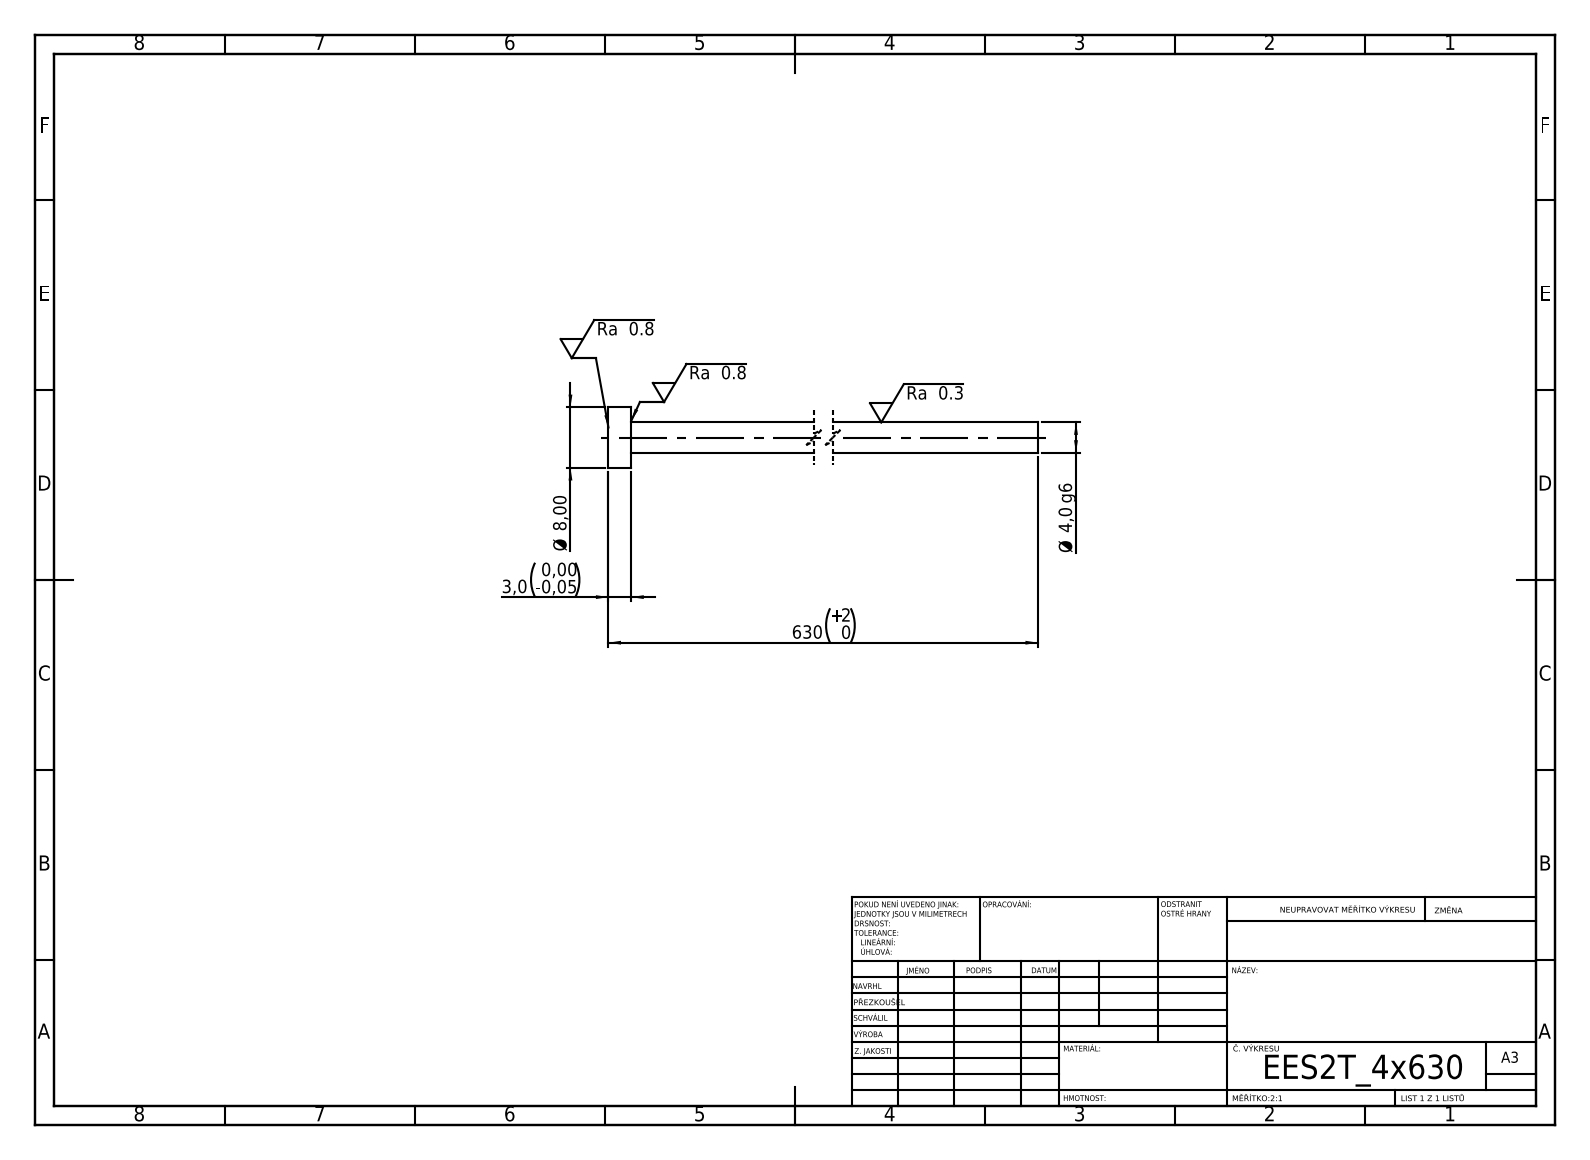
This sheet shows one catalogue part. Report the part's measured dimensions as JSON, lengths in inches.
{"step_written_by": "SolidWorks 2019 (CONFIG_CONTROL_DESIGN)", "units": "inches", "bodies": {"solids": 1, "faces": 7, "planar": 3, "cylindrical": 4, "other": 0}, "overall_size": [24.803, 0.315, 0.315], "volume_in3": 0.49, "surface_area_in2": 12.49, "round_bosses_or_shafts": [[0.315, 1], [0.157, 1]], "face_to_face_distances": [0.118, 24.803, 24.685]}
